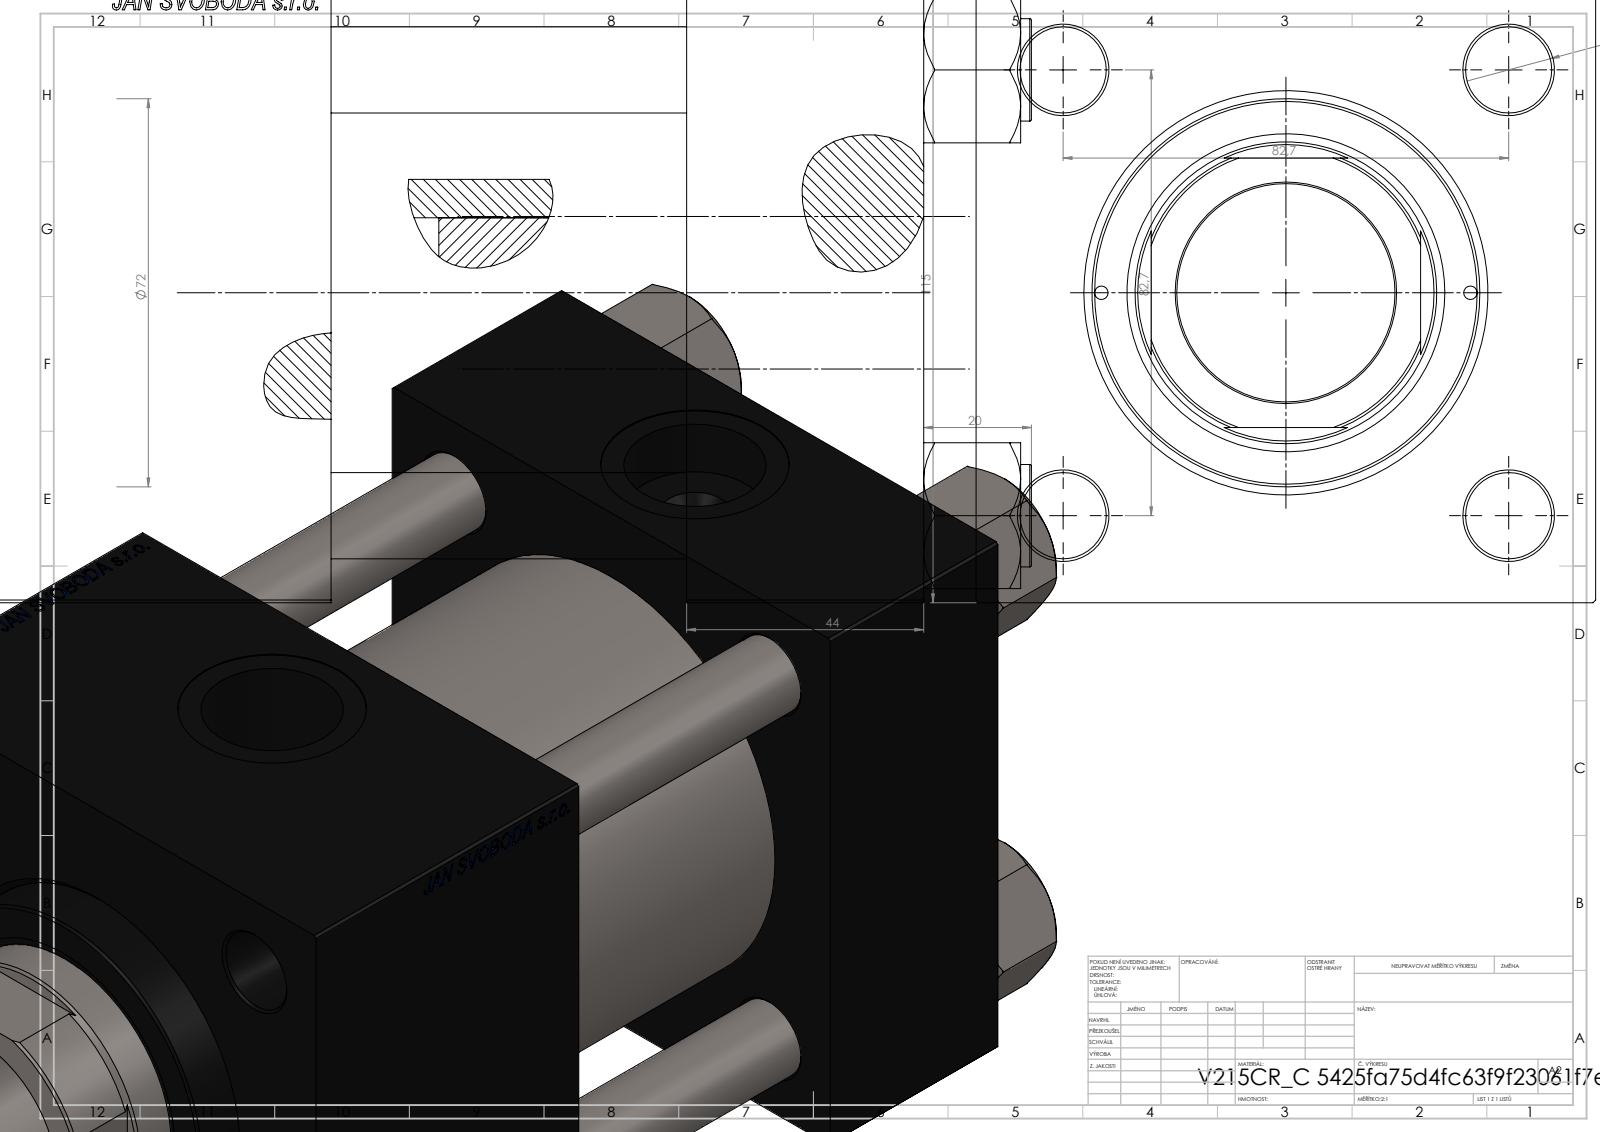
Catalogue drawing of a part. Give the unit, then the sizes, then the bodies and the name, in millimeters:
Units: millimetres
Overall size (bounding box): 230 × 115 × 115
Round holes (diameter × count): ⌀16 ×4, ⌀2.5 ×2, ⌀7 ×2, ⌀26.44 ×2, ⌀35 ×2, ⌀40.5 ×1, ⌀56 ×1, ⌀59 ×1, ⌀61 ×1, ⌀72 ×1, ⌀80 ×1
Round bosses / shafts (diameter × count): ⌀19 ×4, ⌀86 ×1
Partial cylindrical surfaces — rounded edges, fillets, slot ends (radius × count): R27 ×1
Main face-to-face distances: 115, 44, 110, 66, 179, 135, 69, 20, 150.3, 106.3
Hole centre spacings: 41.96, 58.48, 82.7, 86.17, 34.25, 116.96, 68.5, 111
Volume: 1 862 000 mm³ · Surface area: 280 443 mm²
Bodies: 11 solids, 1200 faces (575 planar, 89 cylindrical, 536 other)
Part name (STEP PRODUCT): V215CR_C_Body; V215CR_VCP_C; NUT_M5_C; V215CR_C_TYCINKA (+1 more)
STEP written by: SolidWorks 2019 (CONFIG_CONTROL_DESIGN)
